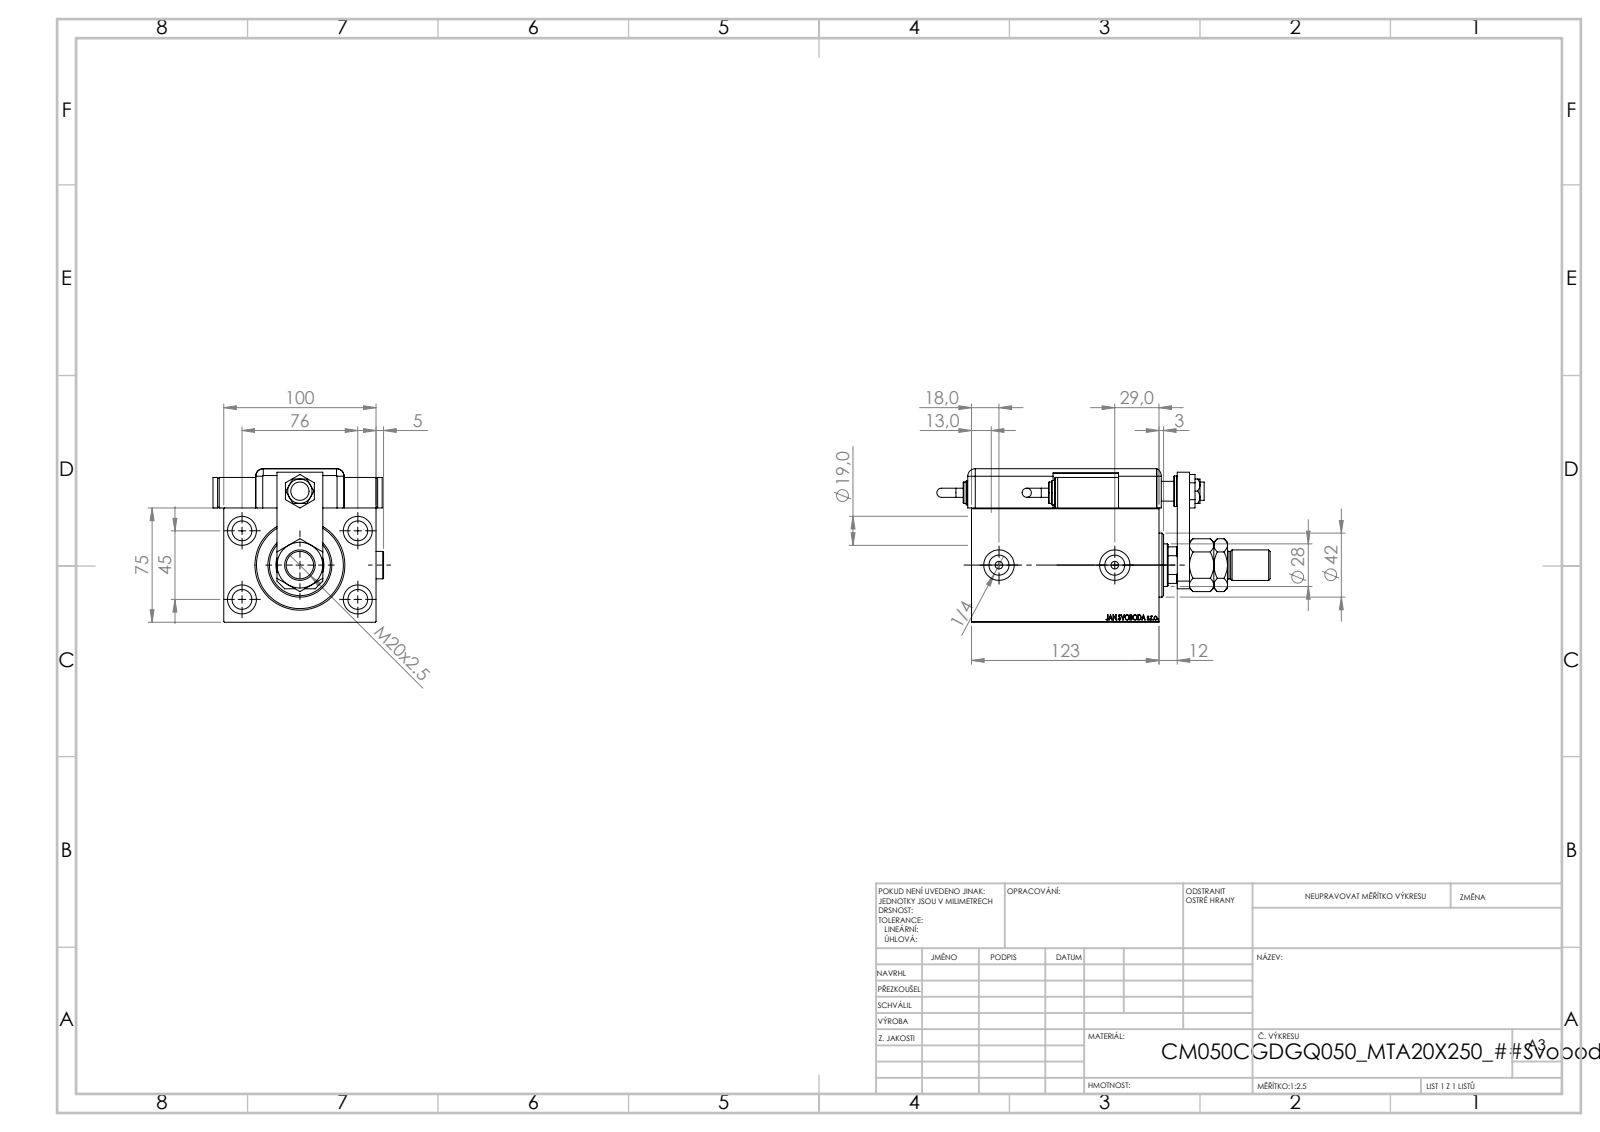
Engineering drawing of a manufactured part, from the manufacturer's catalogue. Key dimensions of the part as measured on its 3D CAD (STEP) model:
Part name (STEP PRODUCT): Zatka_OIL_PORT; TYC; V450CM_C_Body; V450CM_C_VCP (+7 more)
STEP written by: SolidWorks 2019 (CONFIG_CONTROL_DESIGN)
Units: millimetres
Bodies: 16 solids, 1352 faces (664 planar, 137 cylindrical, 551 other)
Overall size (bounding box): 218.76 × 111.9 × 100.8
Volume: 950 881 mm³ · Surface area: 193 782 mm²
Round holes (diameter × count): ⌀13 ×5, ⌀19 ×4, ⌀20 ×3, ⌀4 ×2, ⌀5 ×2, ⌀8 ×2, ⌀13.16 ×2, ⌀12 ×1, ⌀14 ×1, ⌀18.5 ×1, ⌀28 ×1, ⌀31.5 ×1
Round bosses / shafts (diameter × count): ⌀20 ×3, ⌀18 ×3, ⌀16 ×2, ⌀14 ×2, ⌀6 ×2, ⌀42 ×1
Partial cylindrical surfaces — rounded edges, fillets, slot ends (radius × count): R5 ×9, R10 ×1, R13.5 ×1
Main face-to-face distances: 75, 3, 100, 14, 20, 25.8, 100.8, 13.5, 123, 109
Hole centre spacings: 44.16, 76, 45, 46.04, 80.53, 88.32, 20, 48.5
